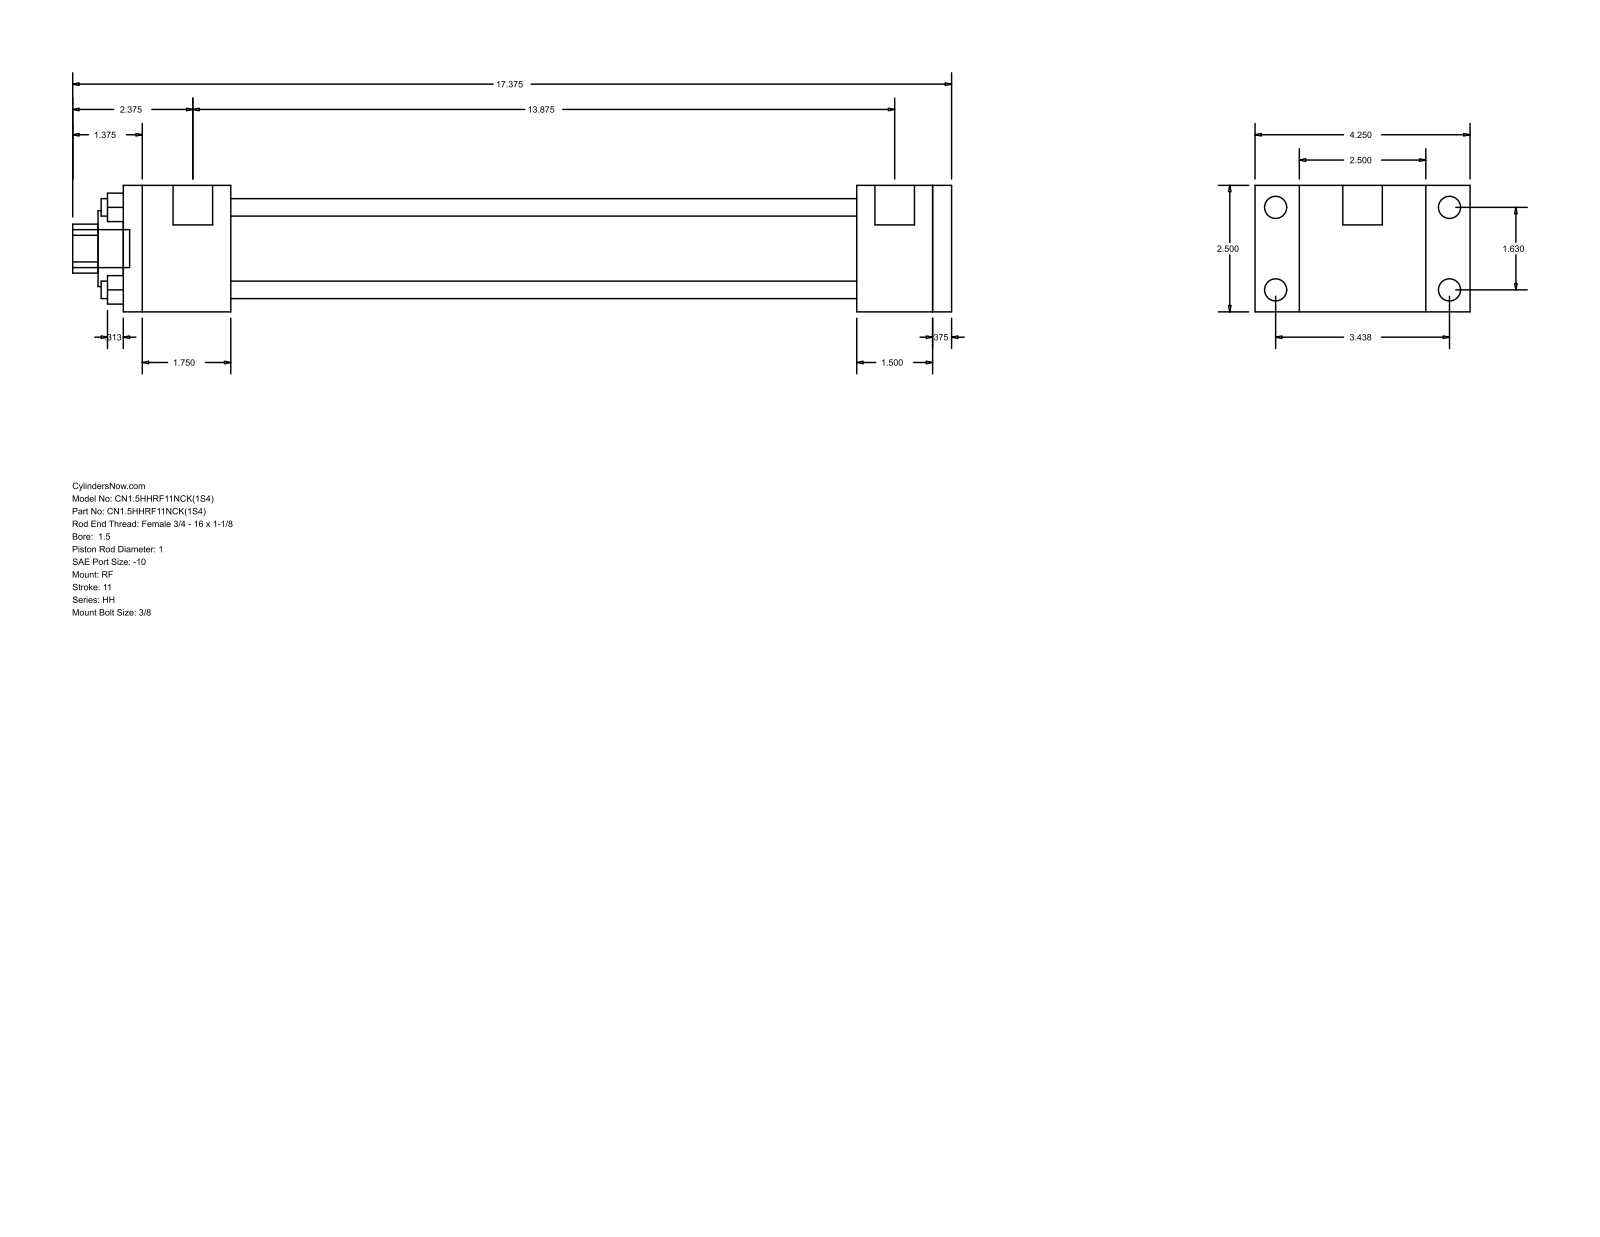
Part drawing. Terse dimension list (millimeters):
name: HH_RF__0150_1
written by: GSSL Pune (CONFIG_CONTROL_DESIGN)
unit: mm
bodies: 0 solids, 92 faces (64 planar, 28 cylindrical, 0 other)
size: 441.32 × 107.95 × 63.5
holes: 4× ⌀8.76, 1× ⌀25.4, 1× ⌀38.1, 1× ⌀44.45
bosses: 4× ⌀11.13, 4× ⌀5.56, 2× ⌀19.84, 1× ⌀19.05
rounds: 1× R12.29
face distances: 63.5, 9.52, 314.32, 352.42, 361.94, 38.1, 47.62, 53.98, 368.3, 406.4
hole spacings: 29.27, 41.4, 58.55
